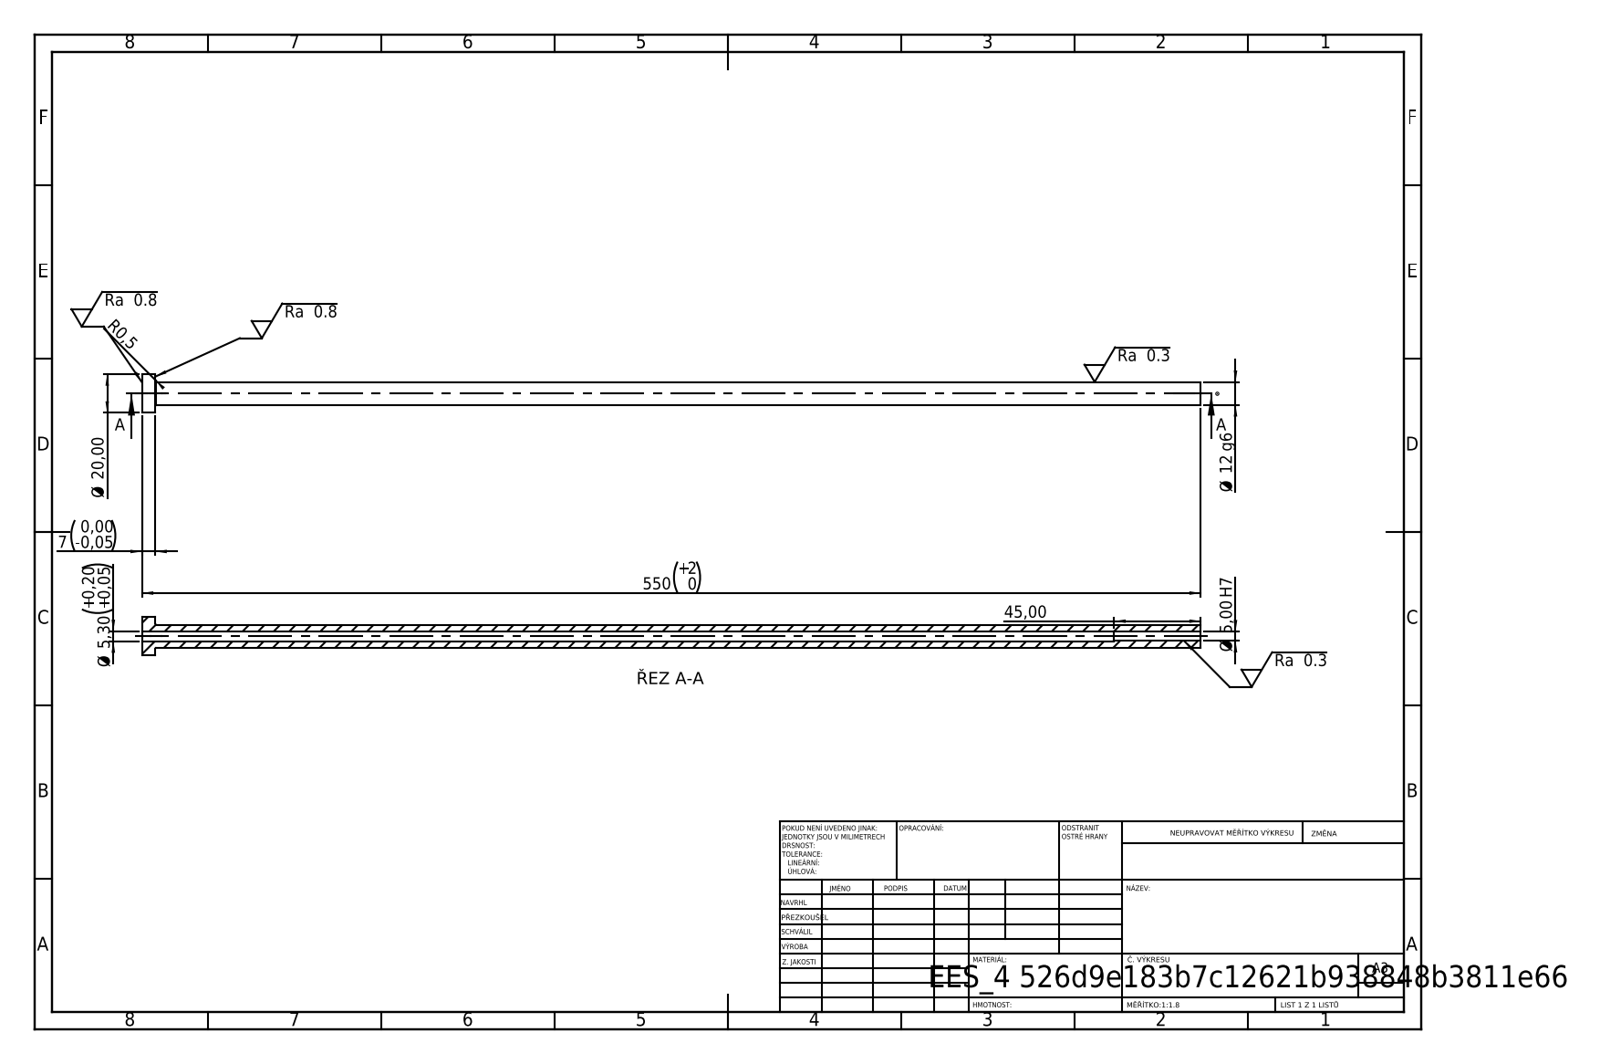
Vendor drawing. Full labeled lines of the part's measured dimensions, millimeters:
STEP written by: SolidWorks 2019 (CONFIG_CONTROL_DESIGN)
Units: millimetres
Bodies: 1 solid, 14 faces (4 planar, 8 cylindrical, 2 other)
Overall size (bounding box): 550 × 20 × 20
Volume: 51 588 mm³ · Surface area: 30 607 mm²
Round holes (diameter × count): ⌀5 ×1, ⌀5.3 ×1
Round bosses / shafts (diameter × count): ⌀20 ×1, ⌀12 ×1
Main face-to-face distances: 7, 550, 543, 505, 498, 45
